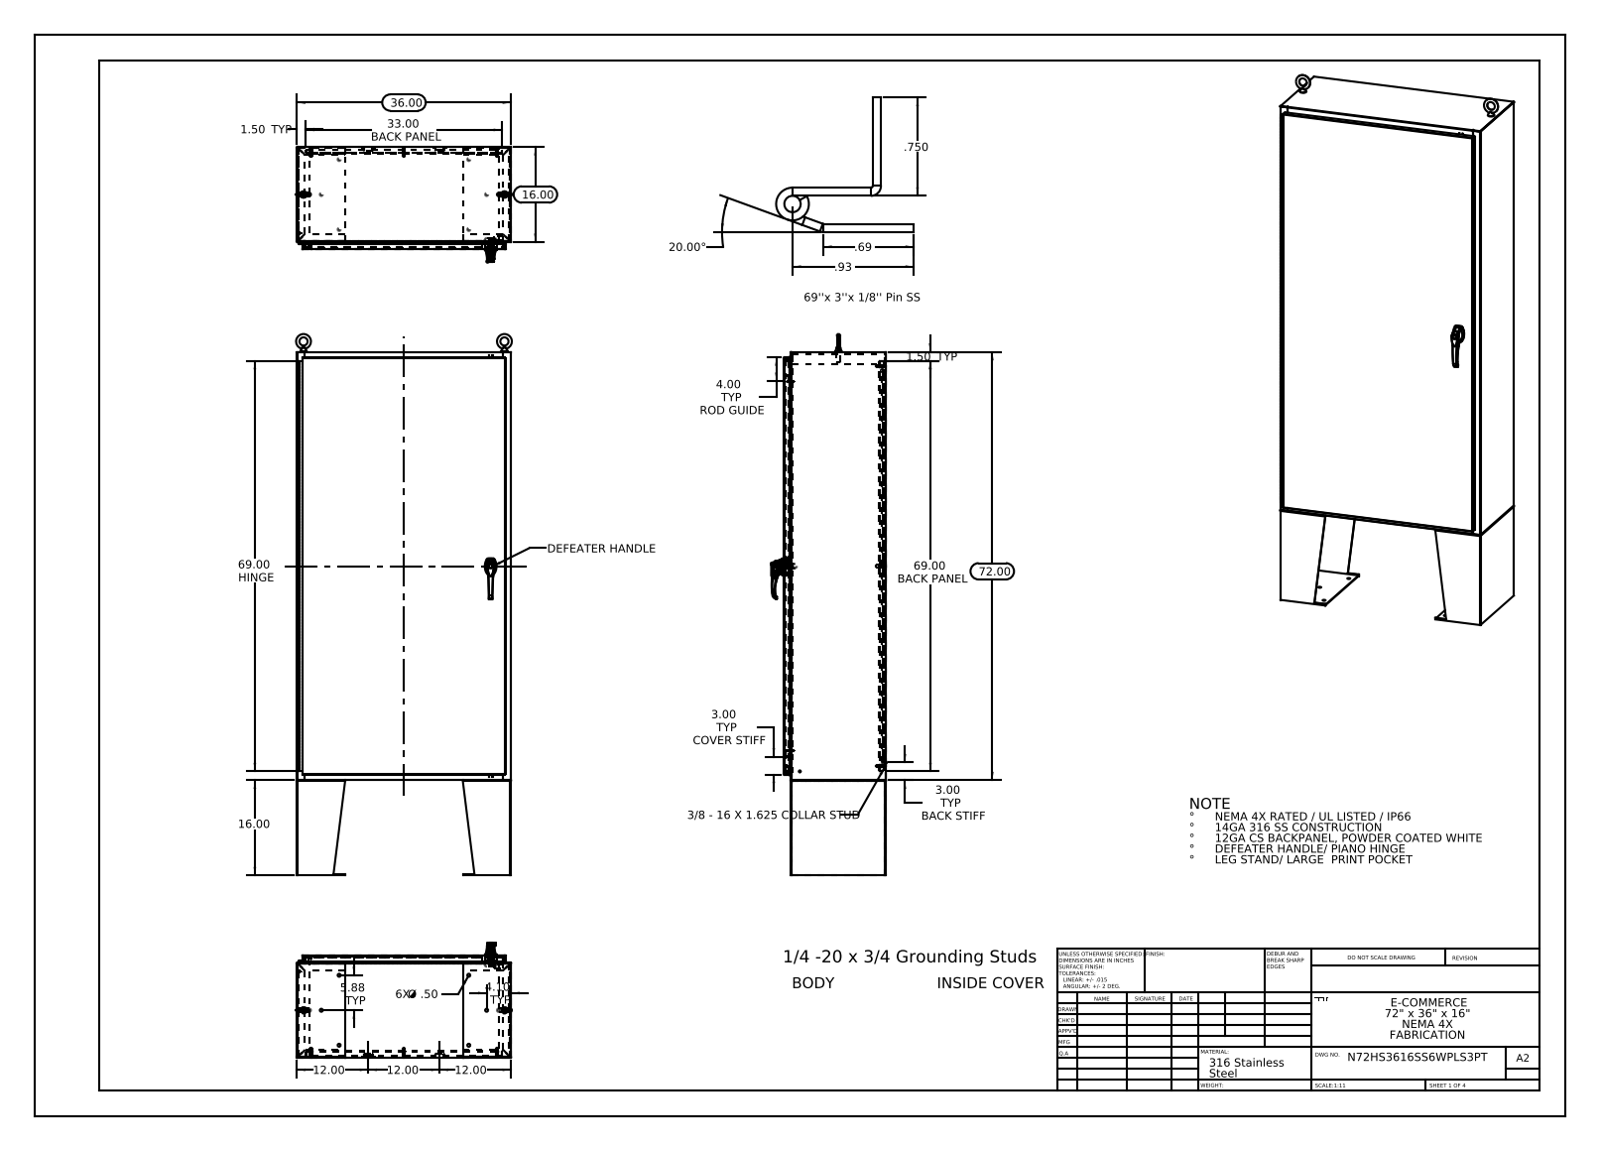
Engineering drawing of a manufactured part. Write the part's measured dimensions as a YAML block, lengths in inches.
part_name: "N72HS3616SSWPLS3PT Mounting Studs; 21130102; N72HS3616SSWPLS3PT SD-LSK - Base; 2616310101 (+8 more)"
step_written_by: "SolidWorks 2013 (CONFIG_CONTROL_DESIGN)"
units: inches
bodies: {solids: 55, faces: 4096, planar: 1673, cylindrical: 1605, other: 818}
overall_size: [91, 36.271, 19.307]
volume: 1156
surface_area: 27891
round_holes:
  - {diameter: 0.5, count: 14}
  - {diameter: 0.25, count: 10}
  - {diameter: 0.75, count: 4}
  - {diameter: 0.138, count: 3}
  - {diameter: 0.161, count: 3}
  - {diameter: 0.079, count: 2}
  - {diameter: 0.203, count: 2}
  - {diameter: 0.313, count: 2}
  - {diameter: 0.437, count: 2}
  - {diameter: 0.125, count: 1}
  - {diameter: 0.125, count: 1}
  - {diameter: 0.197, count: 1}
round_bosses_or_shafts:
  - {diameter: 0.625, count: 10}
  - {diameter: 0.157, count: 10}
  - {diameter: 0.14, count: 10}
  - {diameter: 0.375, count: 8}
  - {diameter: 0.33, count: 8}
  - {diameter: 0.315, count: 3}
  - {diameter: 0.236, count: 3}
  - {diameter: 1.181, count: 1}
partial_cylinders:
  - {radius: 0.118, count: 37}
  - {radius: 0.013, count: 34}
  - {radius: 0.006, count: 33}
  - {radius: 0.088, count: 28}
  - {radius: 0.039, count: 15}
  - {radius: 0.028, count: 12}
  - {radius: 0.039, count: 8}
  - {radius: 0.143, count: 8}
face_to_face_distances: [0.075, 17.126, 0.104, 17.051, 1.075, 17.201, 35.925, 1, 16.051, 16.126]
hole_center_spacings: [8.393, 13.578, 25.48, 28.397, 29.353, 31.661, 33.625, 37.078]
